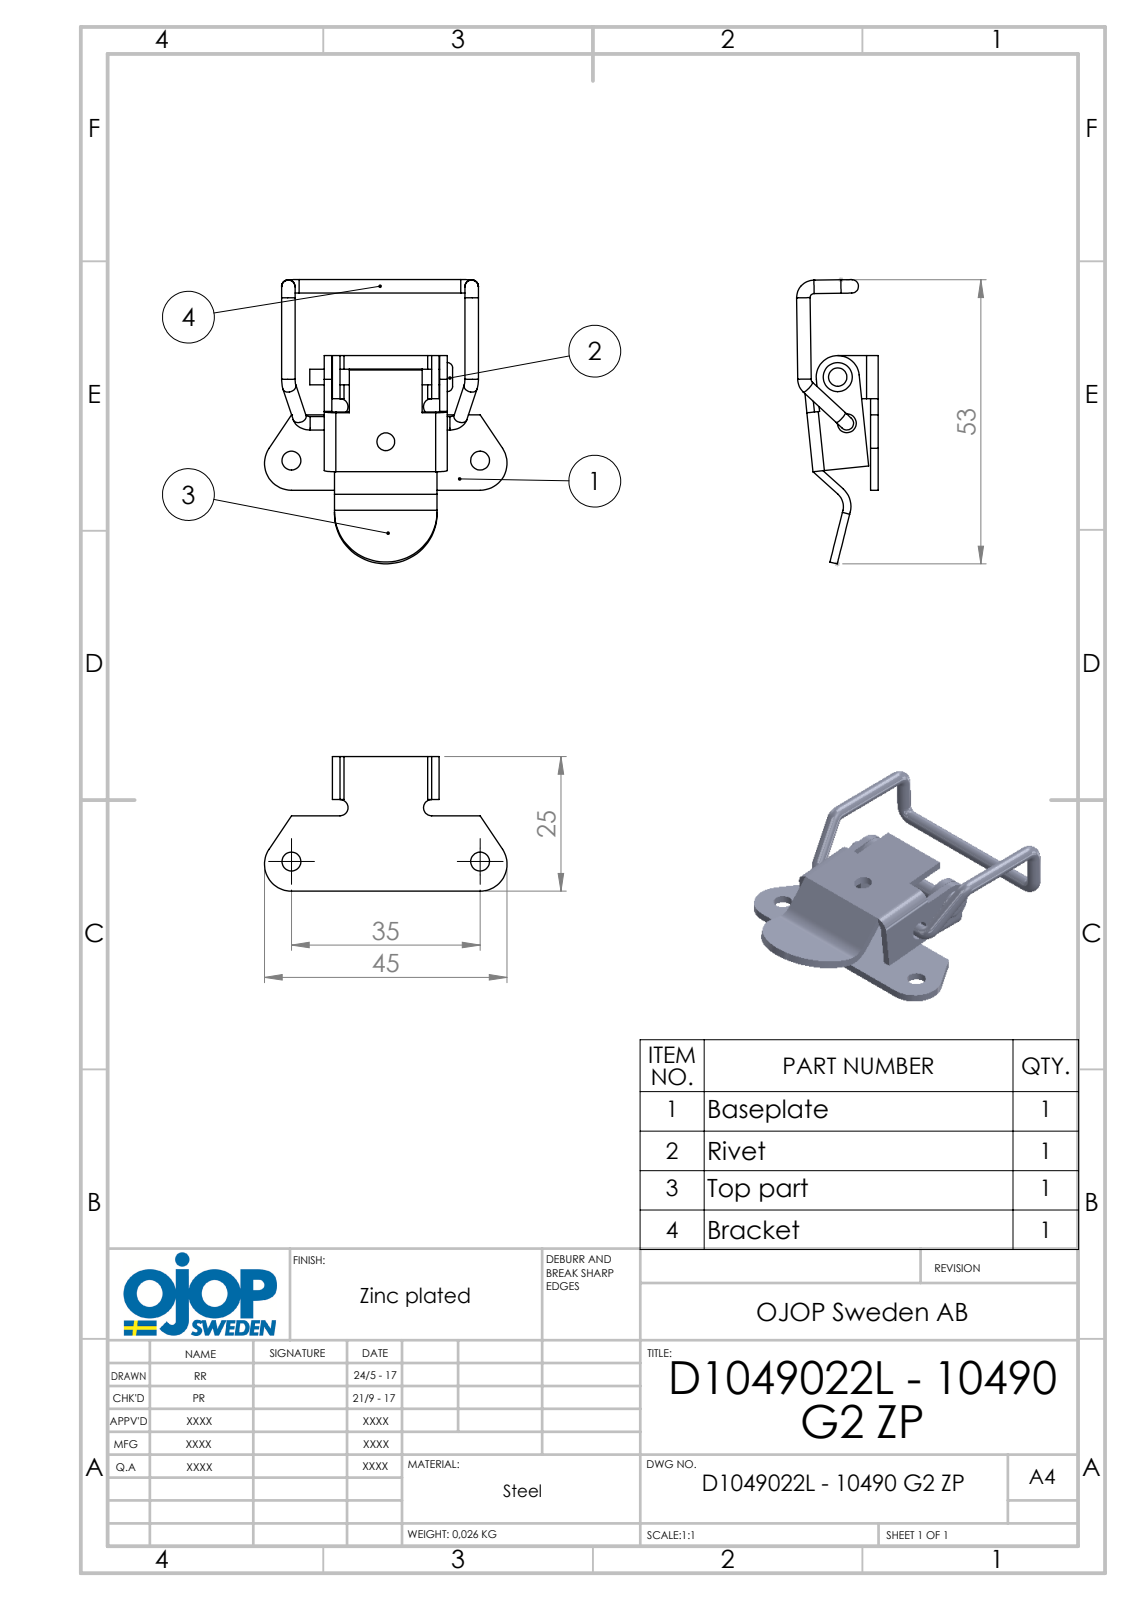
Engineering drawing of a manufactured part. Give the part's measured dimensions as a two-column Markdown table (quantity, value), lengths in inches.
| quantity | value |
| --- | --- |
| part name | överdel; platta; nit; D1049022L - 10490 G2 ZP (+1 more) |
| STEP written by | SolidWorks 2015 (AUTOMOTIVE_DESIGN) |
| units | inches |
| bodies | 4 solids, 137 faces (58 planar, 61 cylindrical, 18 other) |
| overall size | 2.078 × 1.772 × 0.595 |
| volume | 0.206 in³ |
| surface area | 8.671 in² |
| round holes (diameter × count) | 0.138 × 3, 0.126 × 1, 0.13 × 1 |
| round bosses / shafts (diameter × count) | 0.098 × 8, 0.114 × 1 |
| partial cylindrical surfaces (radius × count) | 0.029 × 4, 0.084 × 4, 0.059 × 2, 0.197 × 2, 0.118 × 1, 0.157 × 1, 0.173 × 1, 0.374 × 1 |
| main face-to-face distances | 0.055, 0.843, 0.059, 0.783, 0.898, 0.787, 0.114, 0.839, 0.728, 0.724 |
| hole center spacings | 0.703, 0.344, 1.378 |
